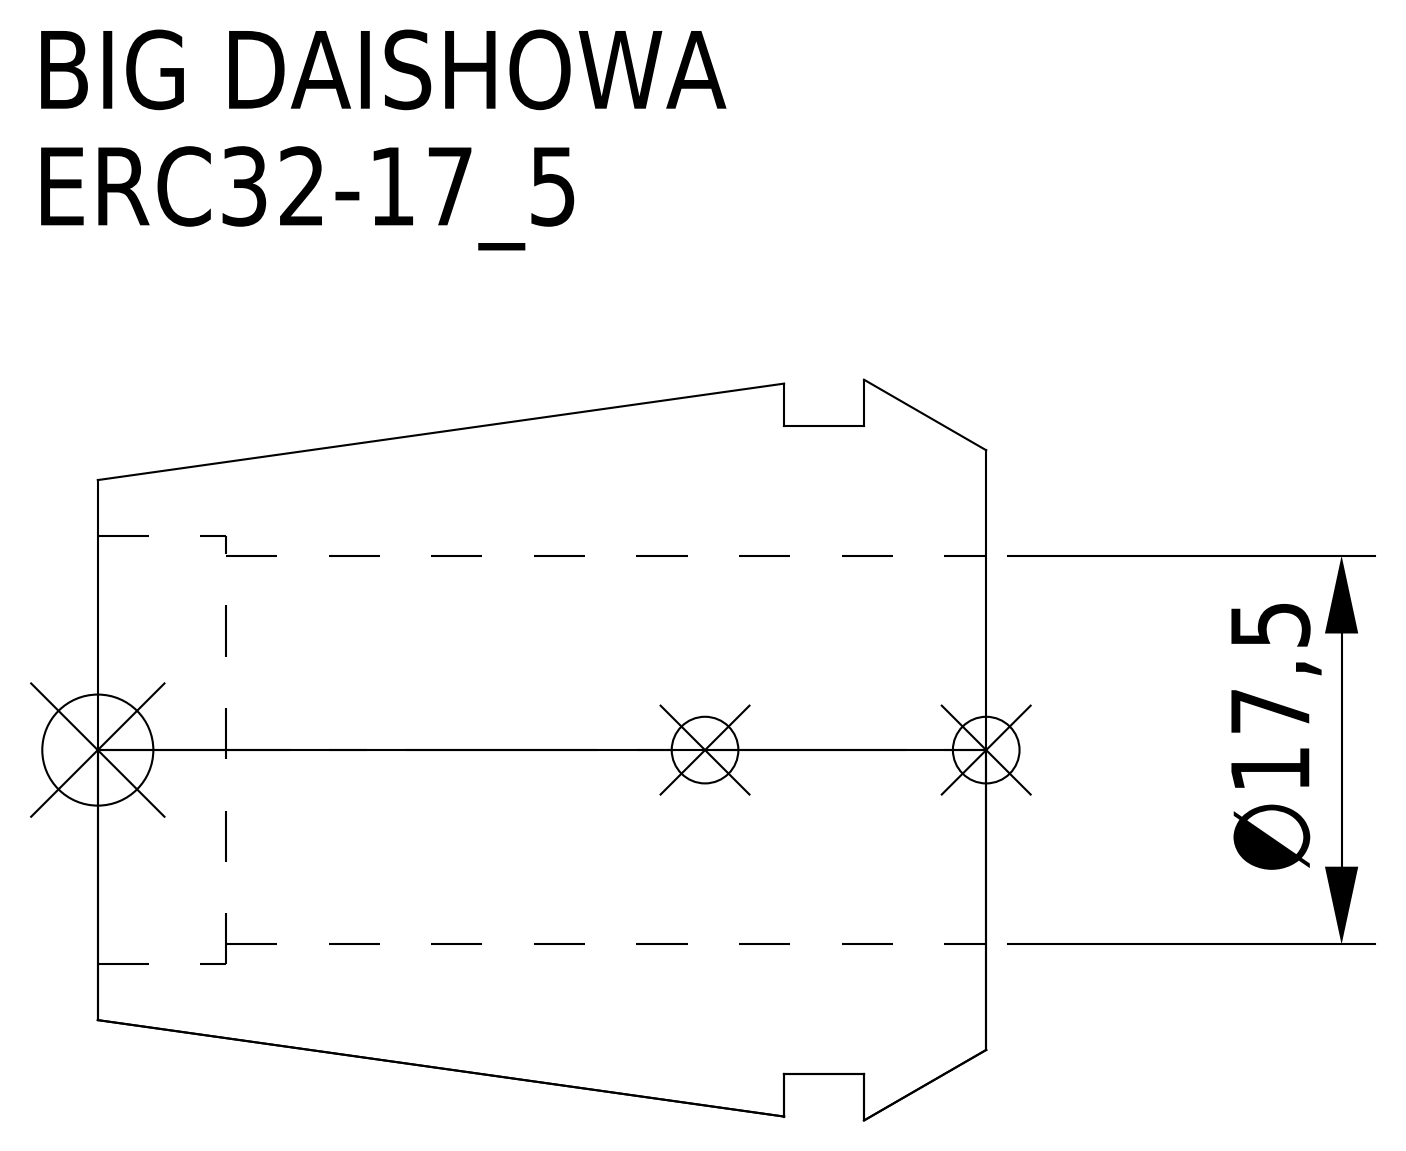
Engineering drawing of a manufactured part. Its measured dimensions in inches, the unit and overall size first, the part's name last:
Units: inches
Overall size (bounding box): 1.575 × 1.313 × 1.313
Round holes (diameter × count): ⌀0.689 ×1, ⌀0.76 ×1
Round bosses / shafts (diameter × count): ⌀1.15 ×1
Main face-to-face distances: 0.217, 0.358, 0.142, 1.575, 1.358, 1.217, 1.348, 1.131, 0.989, 0.227
Volume: 1.008 in³ · Surface area: 10.72 in²
Bodies: 1 solid, 15 faces (5 planar, 6 cylindrical, 4 other)
Part name (STEP PRODUCT): ERC32-17_5
STEP written by: CREO PARAMETRIC BY PTC INC, 2016380 (AUTOMOTIVE_DESIGN)
